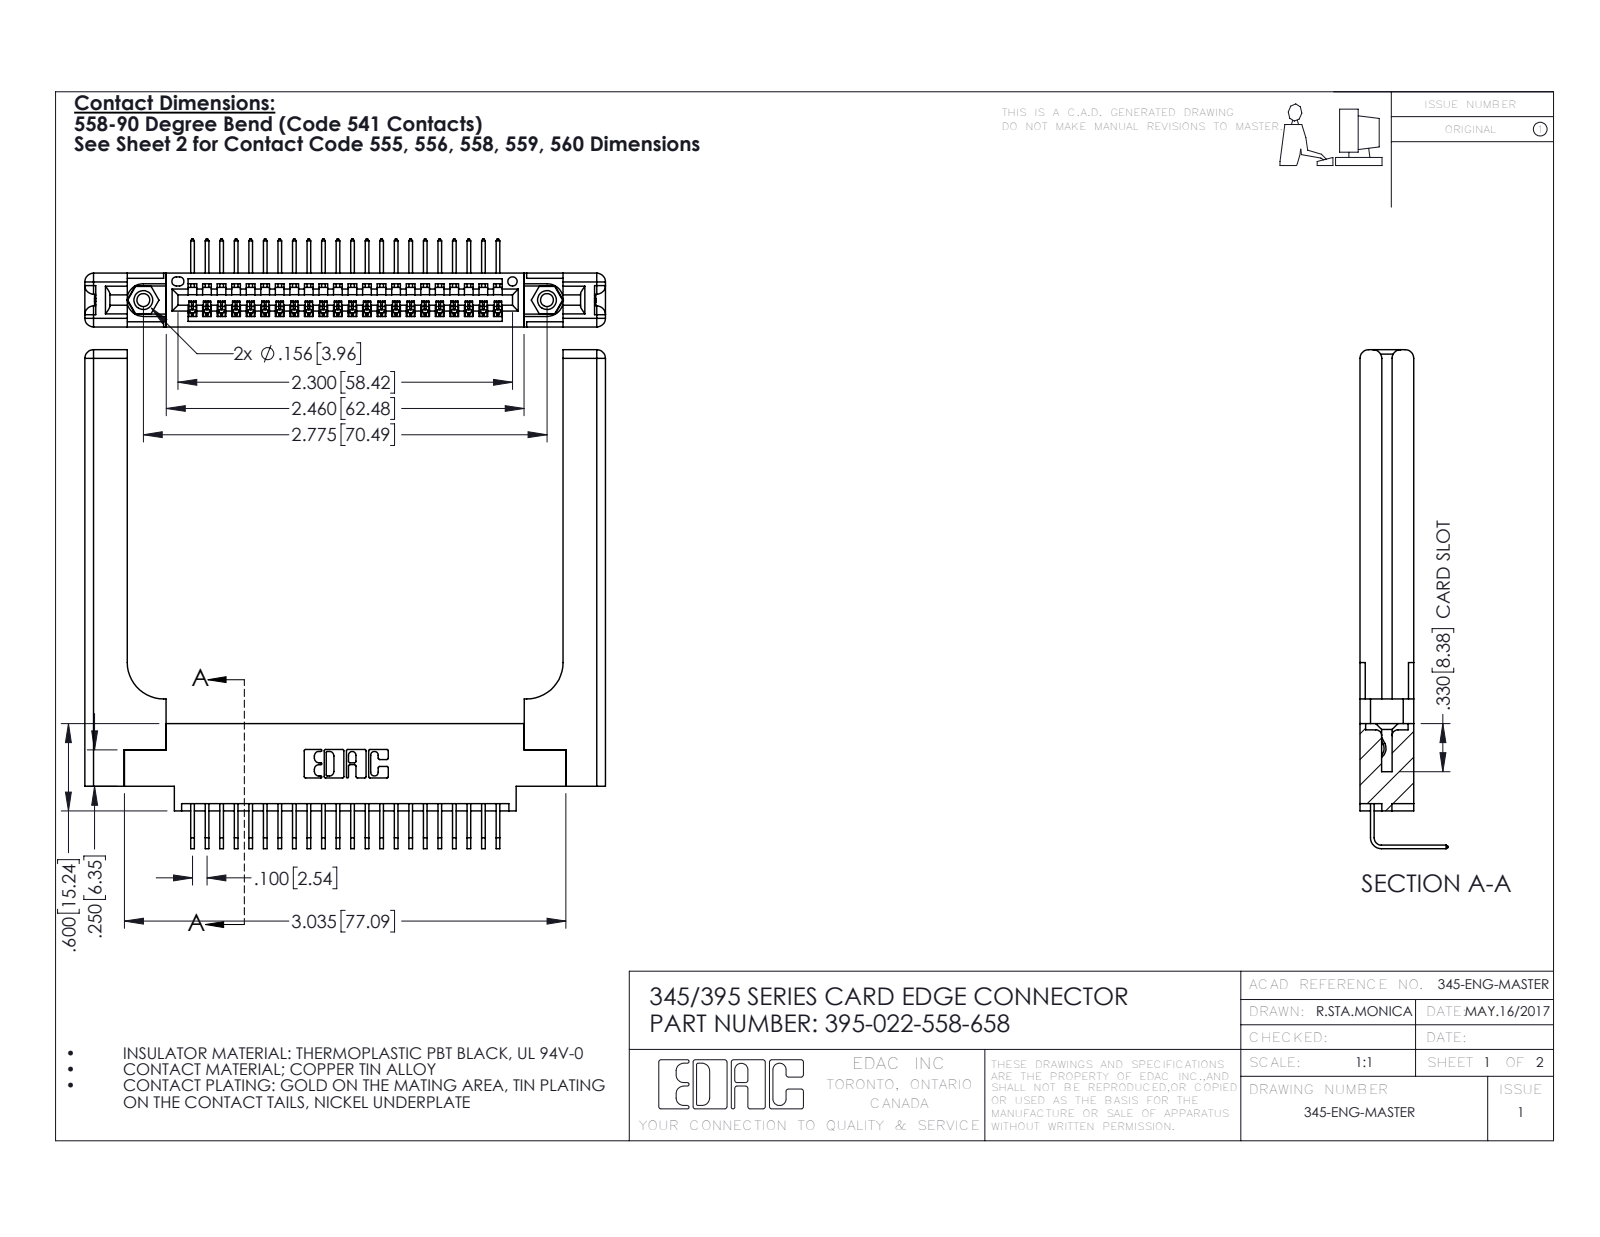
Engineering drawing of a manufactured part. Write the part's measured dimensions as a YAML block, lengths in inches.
part_name: "345-220-058_345-220-058; 345-250-001_345-250-001-102; 395-022-558-658; 345-292-001_558 Tail - 2 (+1 more)"
step_written_by: "SolidWorks 2016 (CONFIG_CONTROL_DESIGN)"
units: inches
bodies: {solids: 27, faces: 1706, planar: 1156, cylindrical: 490, other: 60}
overall_size: [3.579, 3.429, 0.605]
volume: 1.033
surface_area: 26.03
round_holes:
  - {diameter: 0.089, count: 2}
  - {diameter: 0.125, count: 2}
  - {diameter: 0.156, count: 2}
  - {diameter: 0.064, count: 1}
round_bosses_or_shafts:
  - {diameter: 0.155, count: 2}
partial_cylinders:
  - {radius: 0.006, count: 44}
  - {radius: 0.01, count: 22}
  - {radius: 0.06, count: 16}
  - {radius: 0.007, count: 6}
  - {radius: 0.031, count: 6}
  - {radius: 0.026, count: 3}
  - {radius: 0.03, count: 2}
  - {radius: 0.031, count: 2}
face_to_face_distances: [0.37, 0.072, 0.298, 0.15, 0.148, 0.077, 0.22, 0.098, 0.272, 0.025]
hole_center_spacings: [0.27, 2.541, 2.775]
